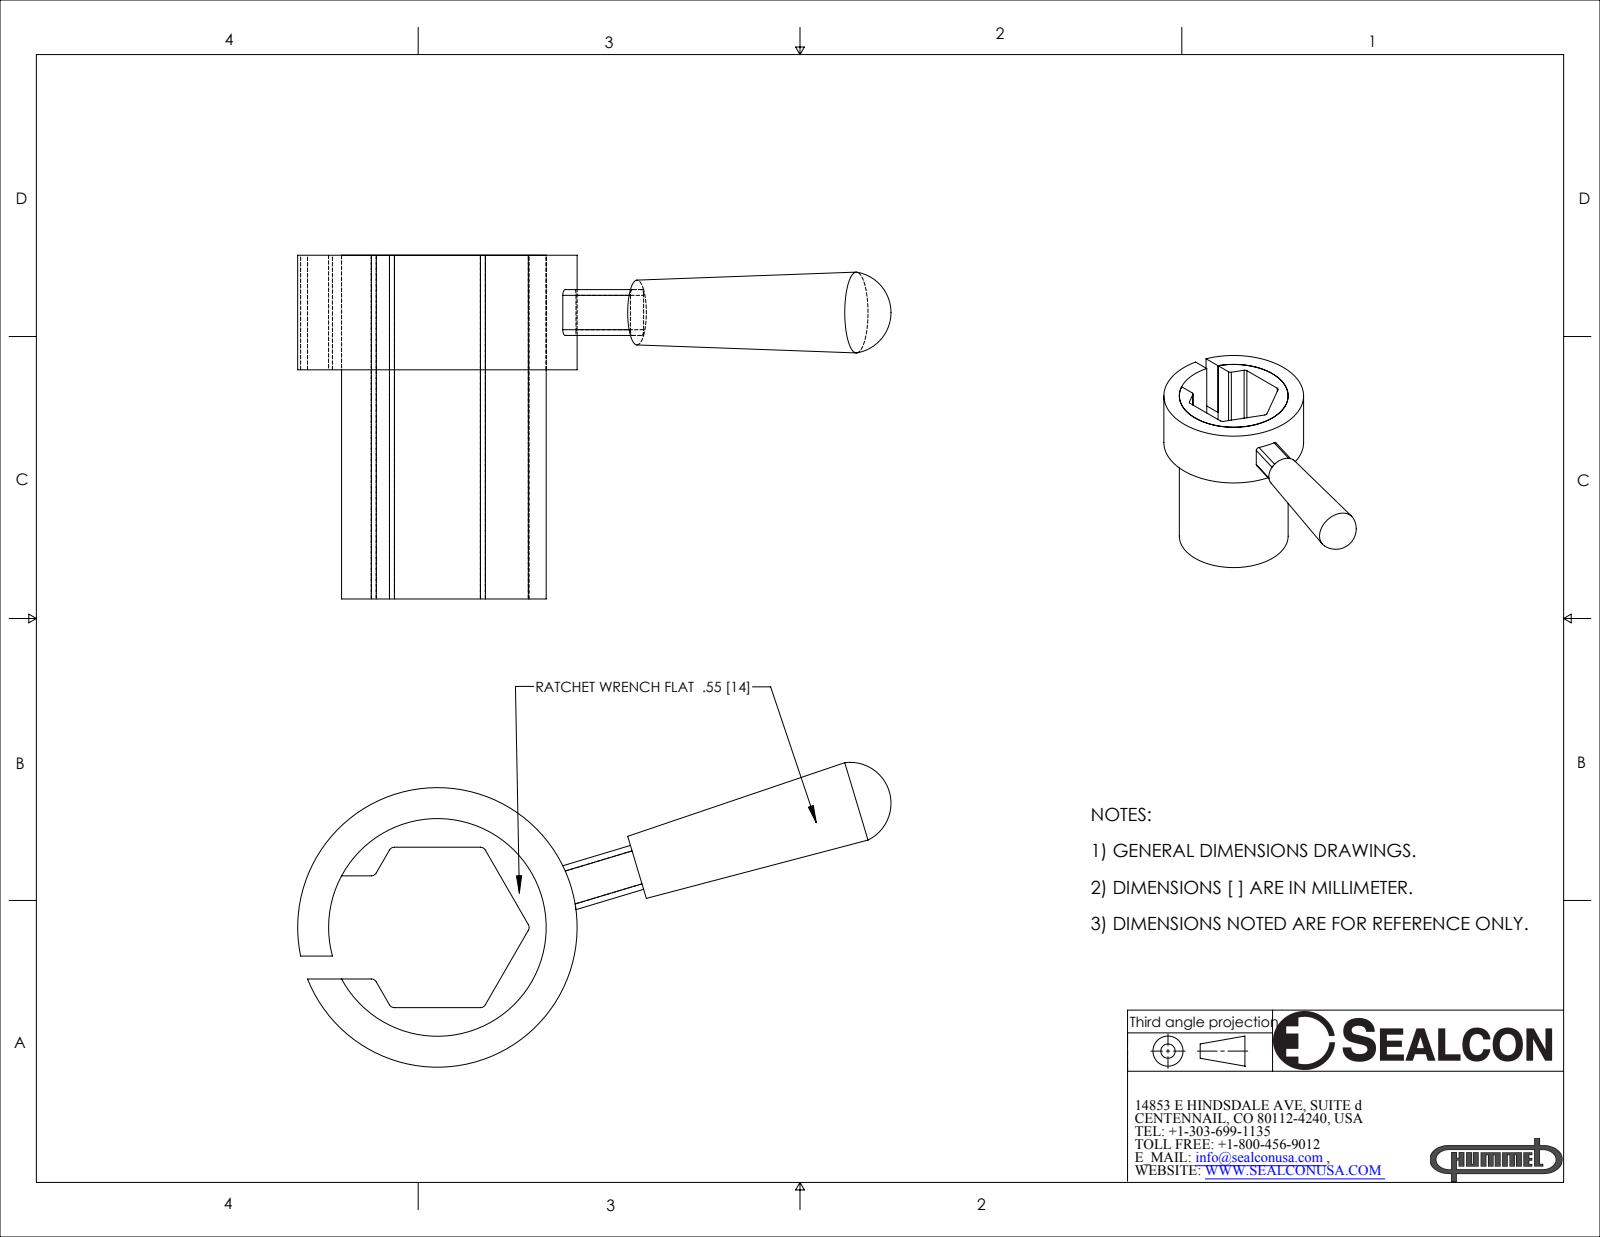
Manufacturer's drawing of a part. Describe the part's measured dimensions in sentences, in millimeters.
The part is named "R-1400-WR". Its 3-D file was written by "SolidWorks 2007 (CONFIG_CONTROL_DESIGN)". It is 3 solids with 43 faces: 19 planar, 20 cylindrical and 4 other. Overall it measures 51.81 by 30 by 26.61 millimeters. Its volume is 5 370 cubic millimeters and its surface area 5 319 square millimeters. Round holes: 1 of diameter 19. Round bosses or shafts: 1 of diameter 24.4. Partial cylindrical surfaces (rounded edges, fillets, slot ends): 11 of radius 0.5. The main face-to-face distances are 14, 2.5, 11.5, 10, 20, 30, 9, 7, 4, 3.
